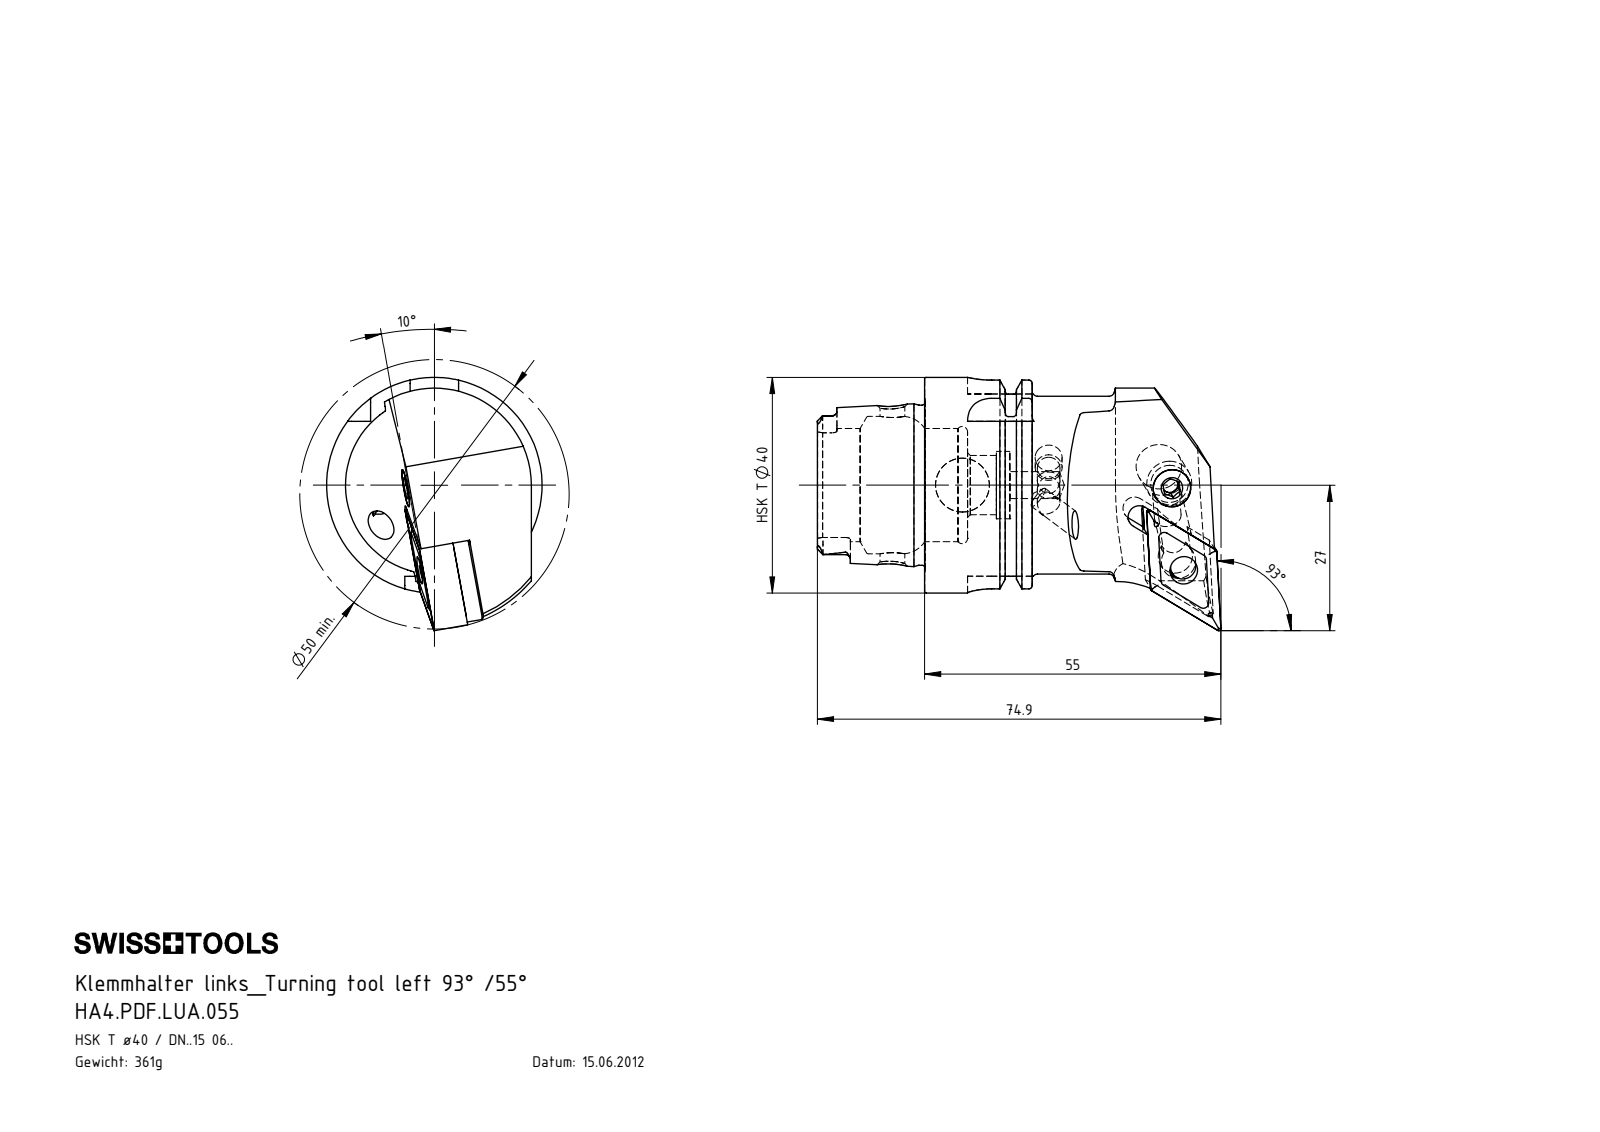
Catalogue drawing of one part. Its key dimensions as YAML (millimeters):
part_name: "HA4-PDF.LUA.055; DNMG150604; WDF-ER2.101.003_A; WCD-ER1.101.000 (+4 more)"
step_written_by: "SolidWorks 2012 (CONFIG_CONTROL_DESIGN)"
units: millimeters
bodies: {solids: 8, faces: 381, planar: 119, cylindrical: 104, other: 158}
overall_size: [74.9, 47, 40]
volume: 46919
surface_area: 17173
round_holes:
  - {diameter: 4.2, count: 2}
  - {diameter: 5, count: 2}
  - {diameter: 6.4, count: 2}
  - {diameter: 4, count: 1}
  - {diameter: 4.6, count: 1}
  - {diameter: 5.16, count: 1}
  - {diameter: 7, count: 1}
  - {diameter: 8.4, count: 1}
  - {diameter: 10, count: 1}
  - {diameter: 11, count: 1}
  - {diameter: 12.5, count: 1}
  - {diameter: 21, count: 1}
round_bosses_or_shafts:
  - {diameter: 40, count: 1}
  - {diameter: 34.75, count: 1}
  - {diameter: 33, count: 1}
  - {diameter: 29.71, count: 1}
  - {diameter: 8, count: 1}
  - {diameter: 7.9, count: 1}
  - {diameter: 6.4, count: 1}
  - {diameter: 5, count: 1}
partial_cylinders:
  - {radius: 0.9, count: 6}
  - {radius: 0.4, count: 4}
  - {radius: 1, count: 4}
  - {radius: 1.88, count: 4}
  - {radius: 4.5, count: 4}
  - {radius: 2.5, count: 2}
  - {radius: 0.8, count: 1}
  - {radius: 2.1, count: 1}
face_to_face_distances: [6.05, 7.95, 19.95, 12, 3.17, 9.22, 19.9, 27.85, 39.85, 3.18]
hole_center_spacings: [15.61, 15.6]
